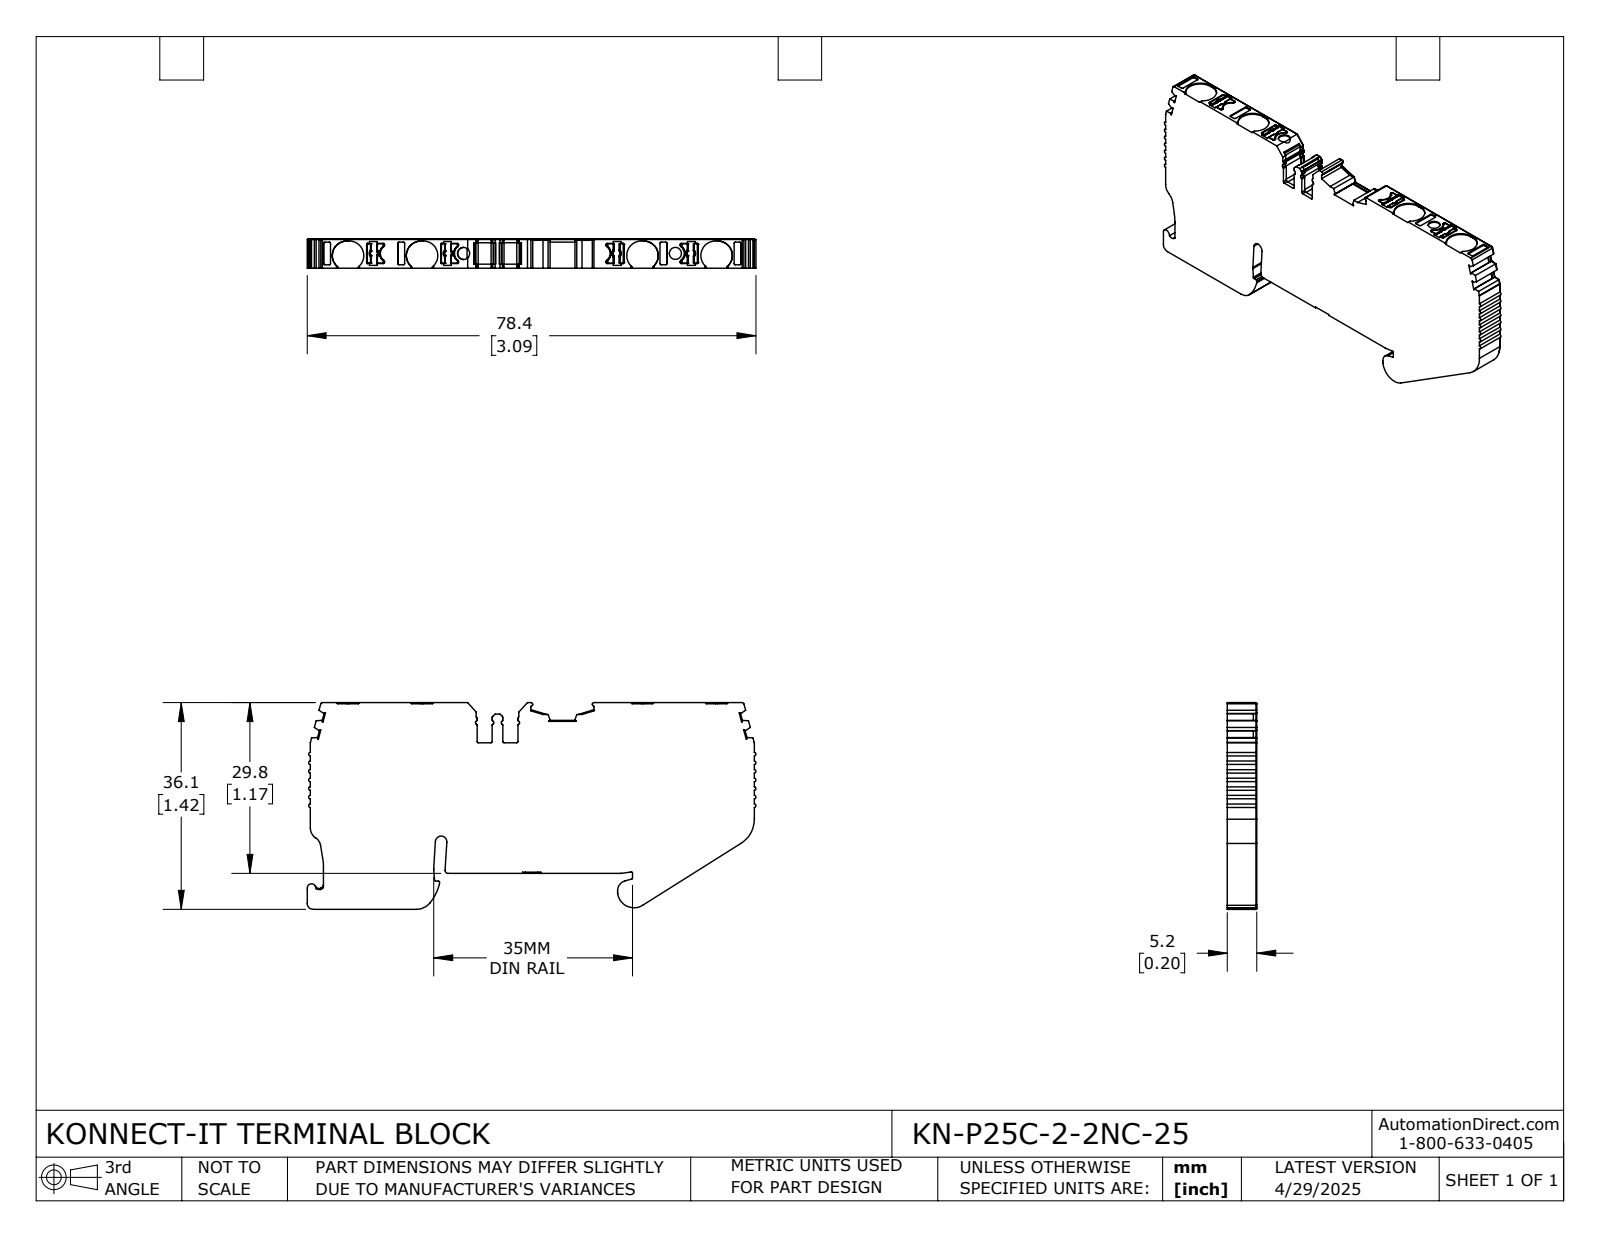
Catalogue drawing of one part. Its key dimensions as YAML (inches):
part_name: "KN-P25C-2-2NC-25"
step_written_by: "SolidWorks 2024 (CONFIG_CONTROL_DESIGN)"
units: inches
bodies: {solids: 1, faces: 739, planar: 381, cylindrical: 291, other: 67}
overall_size: [3.085, 1.42, 0.203]
volume: 0.731
surface_area: 9.638
round_holes:
  - {diameter: 0.083, count: 2}
partial_cylinders:
  - {radius: 0.008, count: 78}
  - {radius: 0.012, count: 39}
  - {radius: 0.004, count: 21}
  - {radius: 0.02, count: 18}
  - {radius: 0.006, count: 16}
  - {radius: 0.016, count: 9}
  - {radius: 0.1, count: 8}
  - {radius: 0.059, count: 4}
face_to_face_distances: [0.203, 1.166, 1.174, 0.246, 1.412, 1.42, 3.052, 0.047, 0.197, 0.177]
hole_center_spacings: [1.456]
